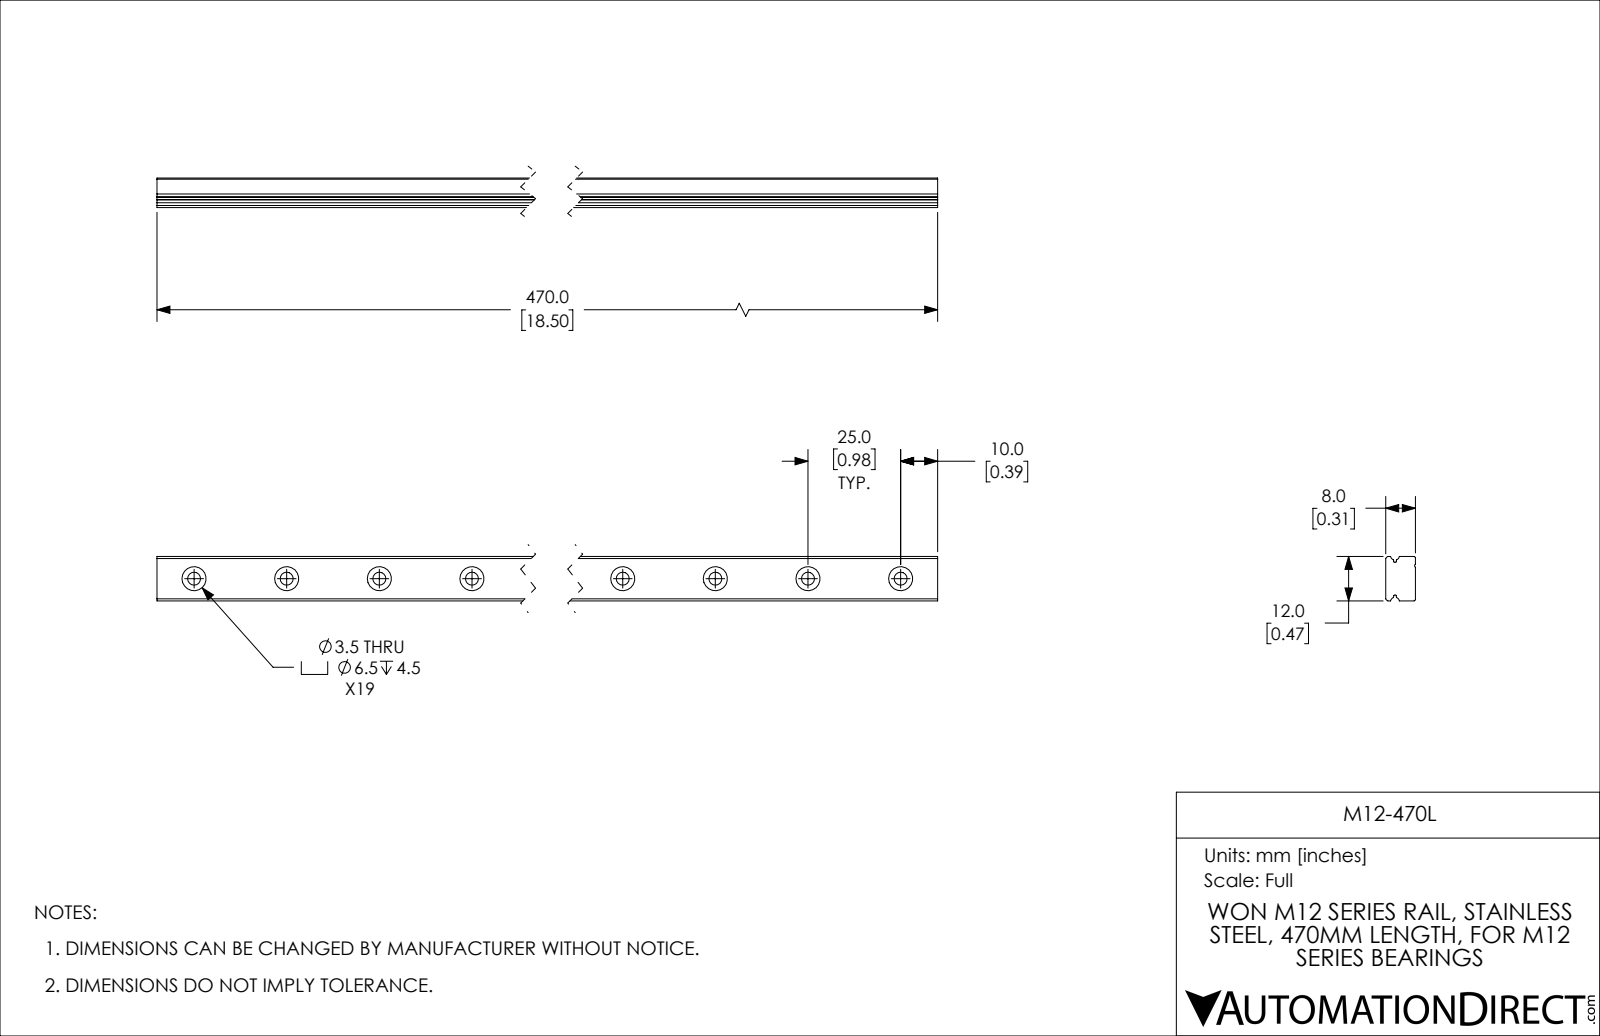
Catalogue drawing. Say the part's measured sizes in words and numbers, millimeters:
The part is named "M12-470L". Its 3-D file was written by "SolidWorks 2019 (CONFIG_CONTROL_DESIGN)". It is 1 solid with 120 faces: 32 planar, 88 cylindrical and 0 other. Overall it measures 470 by 12 by 8 millimeters. Its volume is 39 382 cubic millimeters and its surface area 22 572 square millimeters. Round holes: 19 of diameter 3.5, 19 of diameter 6.5. Partial cylindrical surfaces (rounded edges, fillets, slot ends): 2 of radius 0.42, 2 of radius 1, 2 of radius 1.15, 2 of radius 1.2, 1 of radius 0.5. The main face-to-face distances are 8, 12, 0.58, 3.5, 4.5, 470. The hole center spacings are 25, 50, 75, 100, 125, 150, 175, 200.
